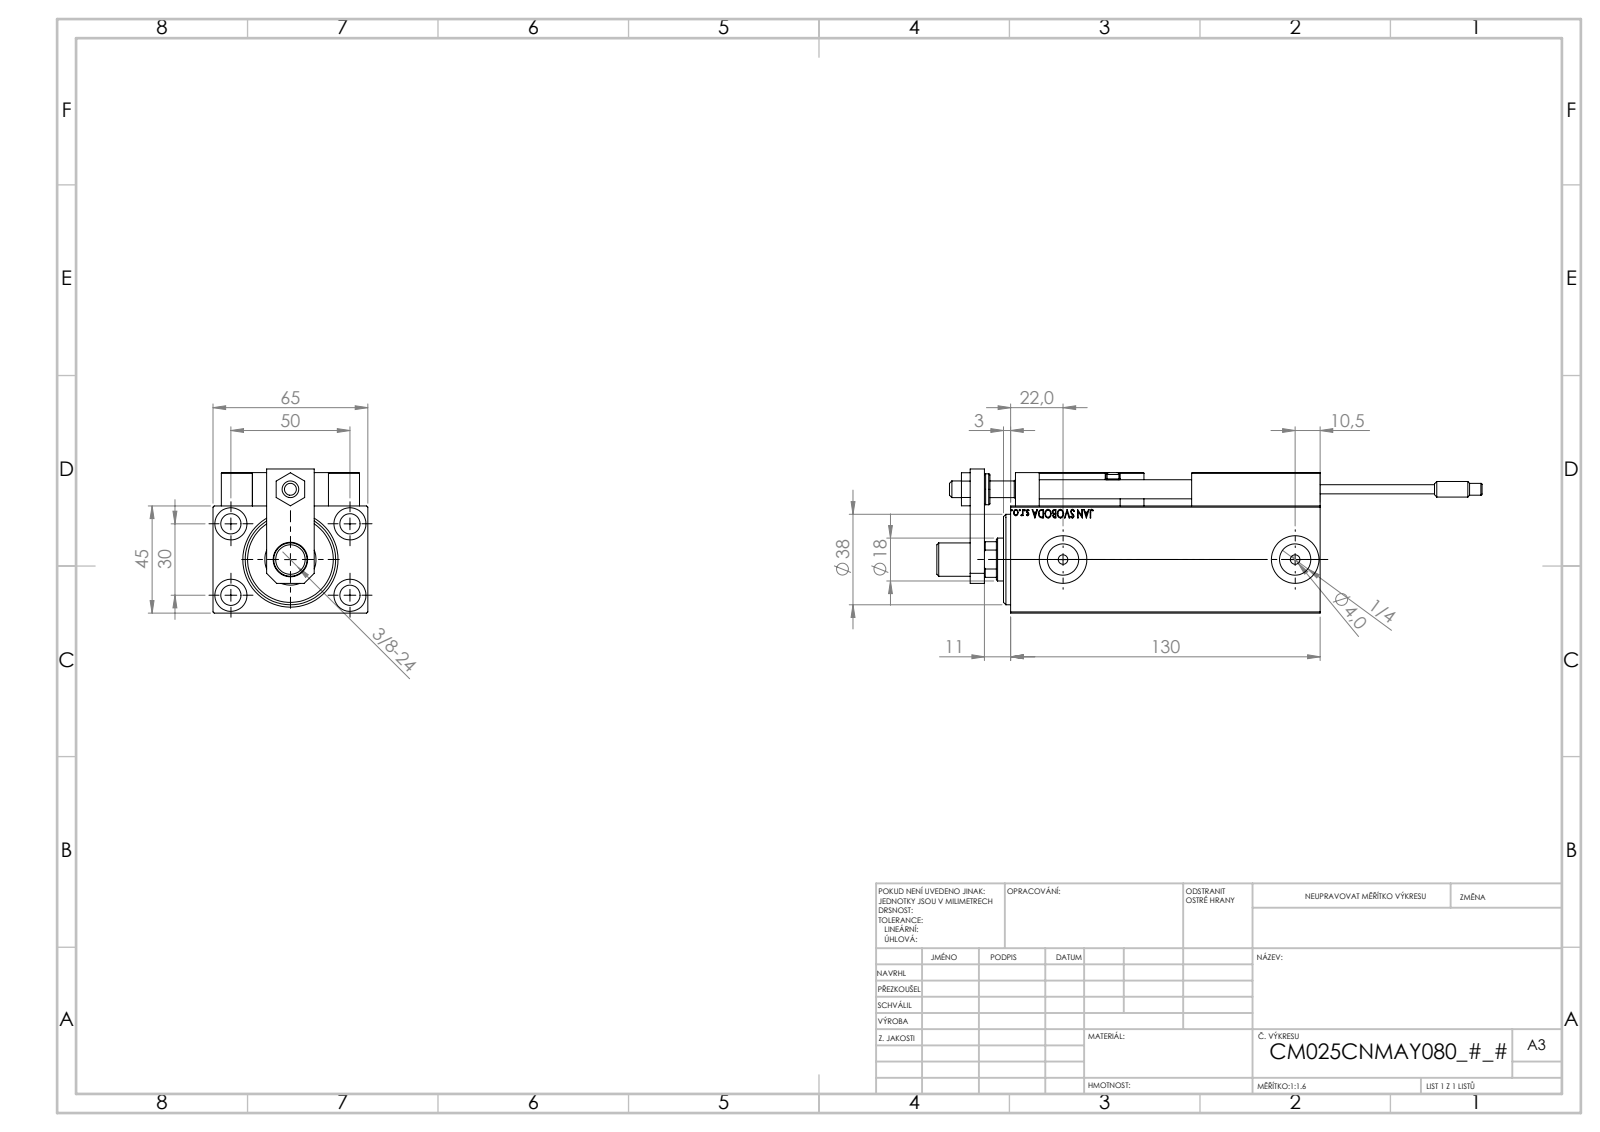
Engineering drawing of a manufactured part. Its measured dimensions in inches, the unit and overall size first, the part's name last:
Units: inches
Overall size (bounding box): 9.016 × 2.559 × 2.382
Round holes (diameter × count): ⌀0.157 ×6, ⌀0.315 ×5, ⌀0.335 ×5, ⌀0.126 ×4, ⌀0.531 ×4, ⌀0.197 ×2, ⌀0.518 ×2, ⌀0.787 ×2, ⌀0.276 ×1, ⌀0.571 ×1, ⌀0.709 ×1, ⌀0.846 ×1
Round bosses / shafts (diameter × count): ⌀0.197 ×4, ⌀0.256 ×2, ⌀0.15 ×2, ⌀0.551 ×1, ⌀0.512 ×1, ⌀0.472 ×1, ⌀0.433 ×1
Partial cylindrical surfaces — rounded edges, fillets, slot ends (radius × count): R0.012 ×30, R0.118 ×2, R0.335 ×1
Main face-to-face distances: 1.772, 2.559, 0.551, 0.236, 2.323, 0.118, 0.787, 5.551, 0.276, 0.512
Hole centre spacings: 1.148, 0.448, 0.787, 1.138, 1.165, 1.169, 1.181, 1.42
Volume: 23.06 in³ · Surface area: 155.5 in²
Bodies: 24 solids, 1317 faces (565 planar, 200 cylindrical, 552 other)
Part name (STEP PRODUCT): KONCOVKA_Y; Block; TYC_L79; V450CM_C_Body (+8 more)
STEP written by: SolidWorks 2019 (CONFIG_CONTROL_DESIGN)
